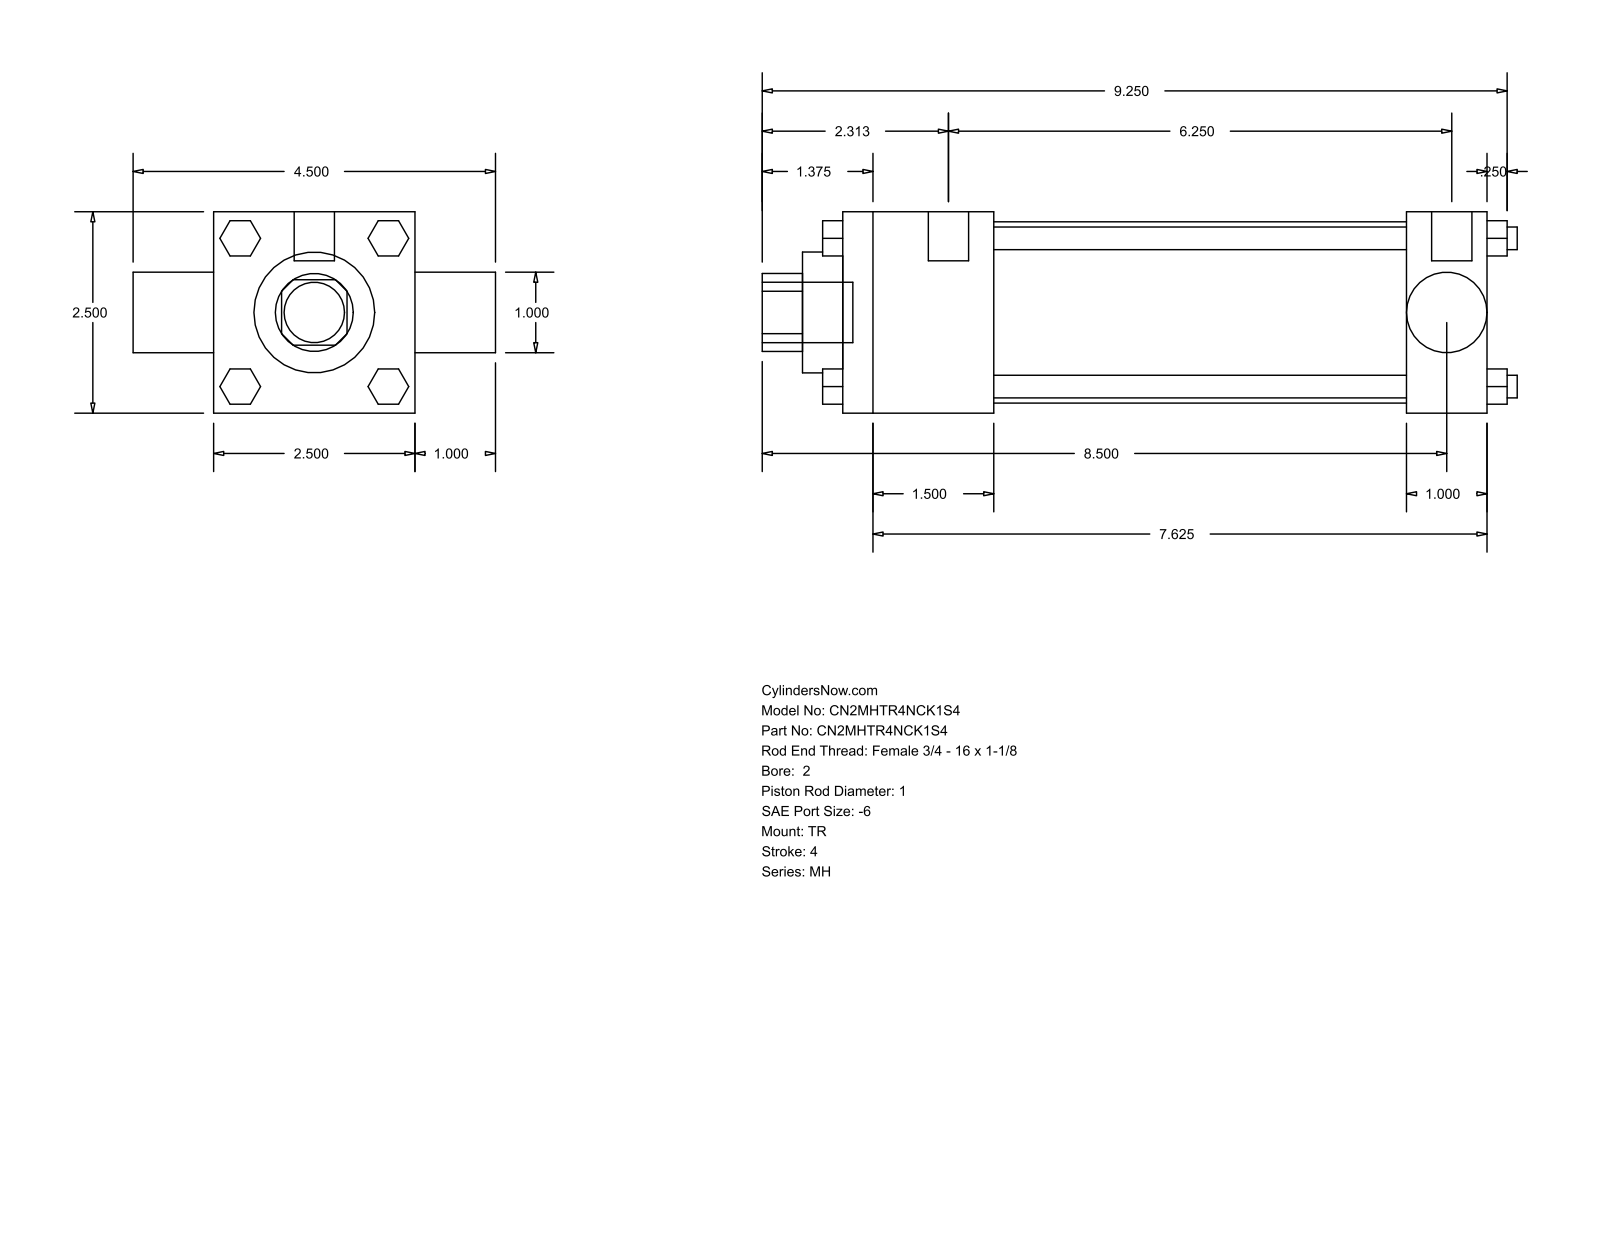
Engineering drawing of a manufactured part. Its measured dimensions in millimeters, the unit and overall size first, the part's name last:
Units: millimetres
Overall size (bounding box): 238.12 × 114.3 × 63.5
Round holes (diameter × count): ⌀25.35 ×1, ⌀25.4 ×1, ⌀38.1 ×1, ⌀57.15 ×1
Round bosses / shafts (diameter × count): ⌀7.14 ×4, ⌀5.56 ×3, ⌀12.7 ×2, ⌀19.05 ×1
Partial cylindrical surfaces — rounded edges, fillets, slot ends (radius × count): R12.29 ×1
Main face-to-face distances: 63.5, 203.2, 25.4, 47.63, 177.8, 130.17, 155.57, 88.9, 215.9, 6.35
Bodies: 0 solids, 120 faces (92 planar, 28 cylindrical, 0 other)
Part name (STEP PRODUCT): MH_TR__0200_1
STEP written by: GSSL Pune (CONFIG_CONTROL_DESIGN)
